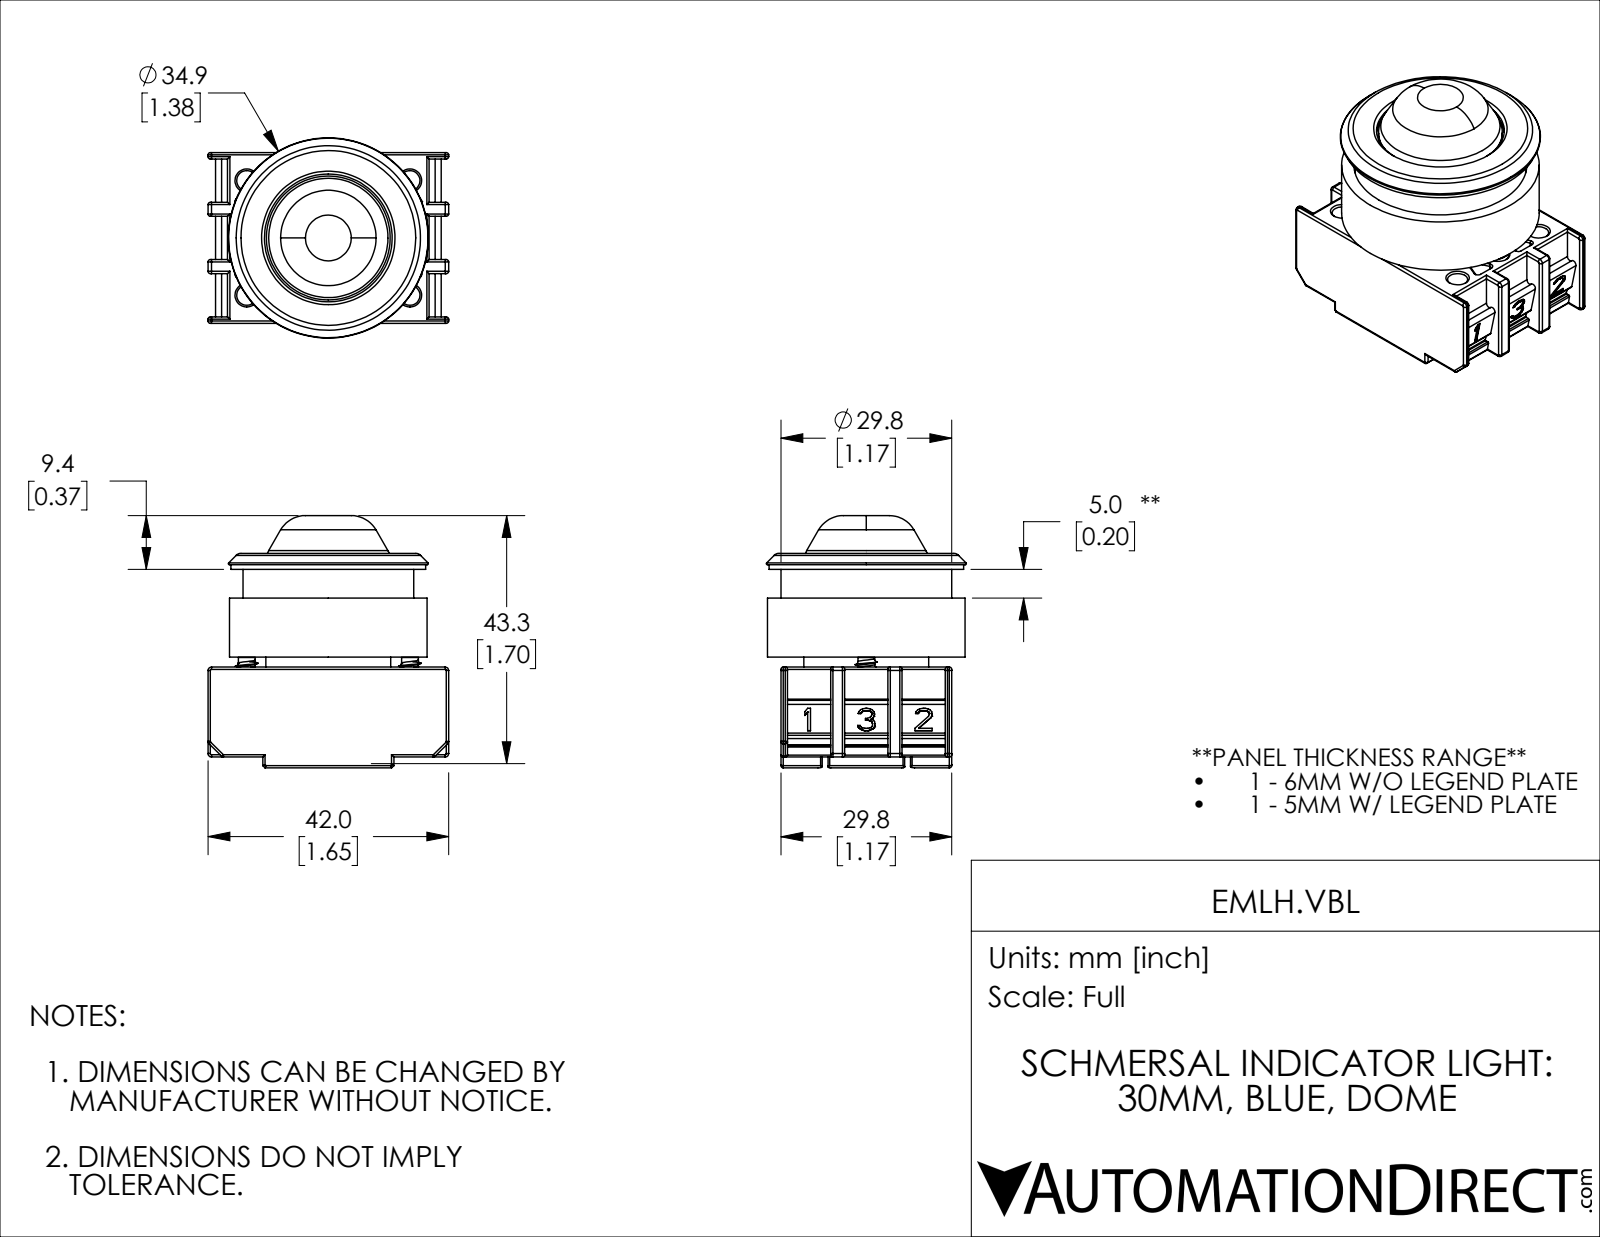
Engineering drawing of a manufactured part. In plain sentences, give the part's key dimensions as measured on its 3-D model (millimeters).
The part is named "EMLH.VBL". Its 3-D file was written by "SolidWorks 2019 (CONFIG_CONTROL_DESIGN)". It is 3 solids with 1622 faces: 641 planar, 498 cylindrical and 483 other. Overall it measures 44.05 by 42 by 34.93 millimeters. Its volume is 22 577 cubic millimeters and its surface area 22 231 square millimeters. Round holes: 6 of diameter 3.5, 6 of diameter 5.15, 1 of diameter 11, 1 of diameter 12.6, 1 of diameter 15, 1 of diameter 18, 1 of diameter 22.3, 1 of diameter 24.2, 1 of diameter 26, 1 of diameter 27, 1 of diameter 30.2. Round bosses or shafts: 2 of diameter 4.8, 2 of diameter 2.93, 1 of diameter 34.5, 1 of diameter 34, 1 of diameter 29.8, 1 of diameter 25.5, 1 of diameter 24.5, 1 of diameter 23.8. Partial cylindrical surfaces (rounded edges, fillets, slot ends): 115 of radius 0.4, 48 of radius 0.3, 28 of radius 0.2, 8 of radius 0.6, 6 of radius 0.5, 2 of radius 0.1, 2 of radius 0.6, 2 of radius 0.8. The main face-to-face distances are 29.8, 1.75, 1.9, 19.35, 19.85, 18.1, 10, 3.4, 7.8, 4.4. The hole center spacings are 10, 17.41, 30.2, 28.5, 14.25, 20, 34.82.
